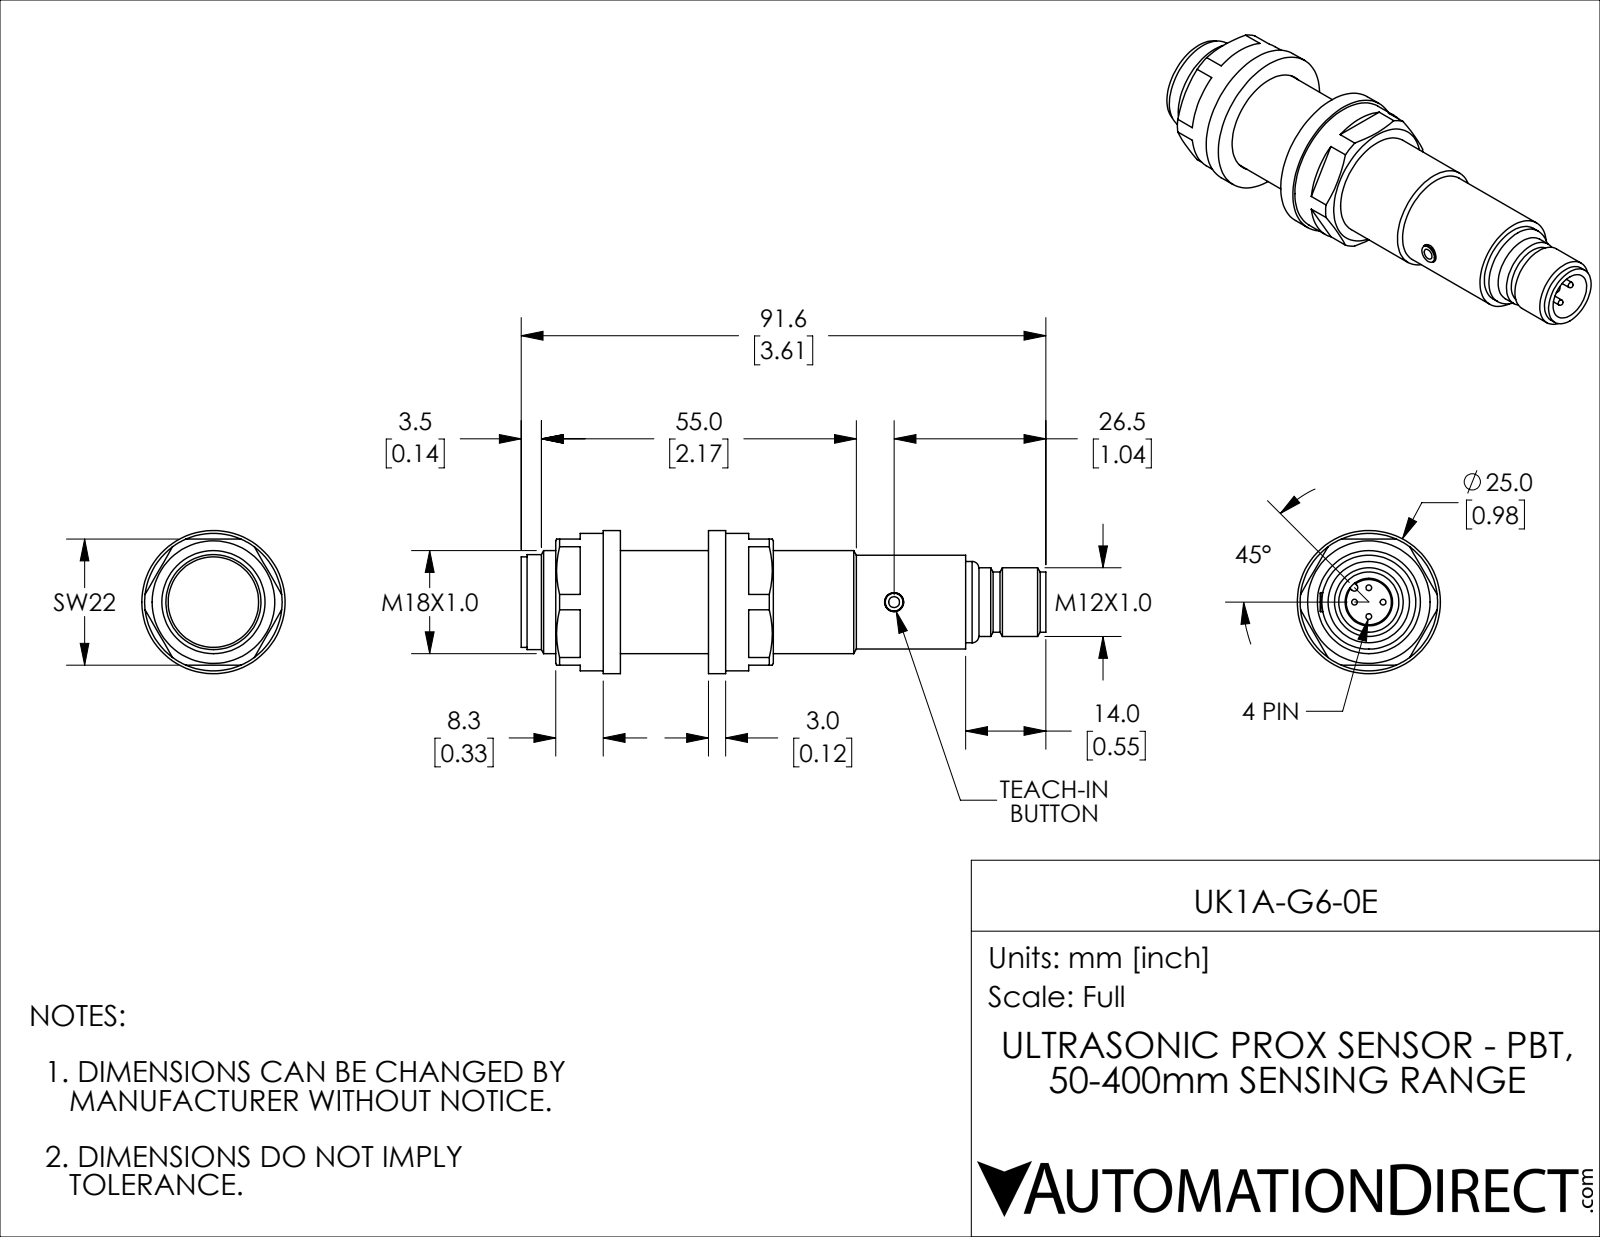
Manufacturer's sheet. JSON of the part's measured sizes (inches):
{"part_name": "UK1A-G6-0E", "step_written_by": "SolidWorks 2018 (AUTOMOTIVE_DESIGN)", "units": "inches", "bodies": {"solids": 6, "faces": 123, "planar": 43, "cylindrical": 49, "other": 31}, "overall_size": [3.606, 0.984, 0.984], "volume_in3": 1.477, "surface_area_in2": 16.01, "round_holes": [[0.13, 1], [0.327, 1], [0.709, 1], [0.717, 1]], "round_bosses_or_shafts": [[0.039, 4], [0.984, 1], [0.945, 1], [0.654, 1], [0.646, 1], [0.622, 1], [0.559, 1], [0.472, 1]], "partial_cylinders_radius": [[0.024, 1]], "face_to_face_distances": [0.118, 0.724, 0.843, 0.606, 0.866, 0.327, 0.445, 1.051, 1.169, 0.563]}
